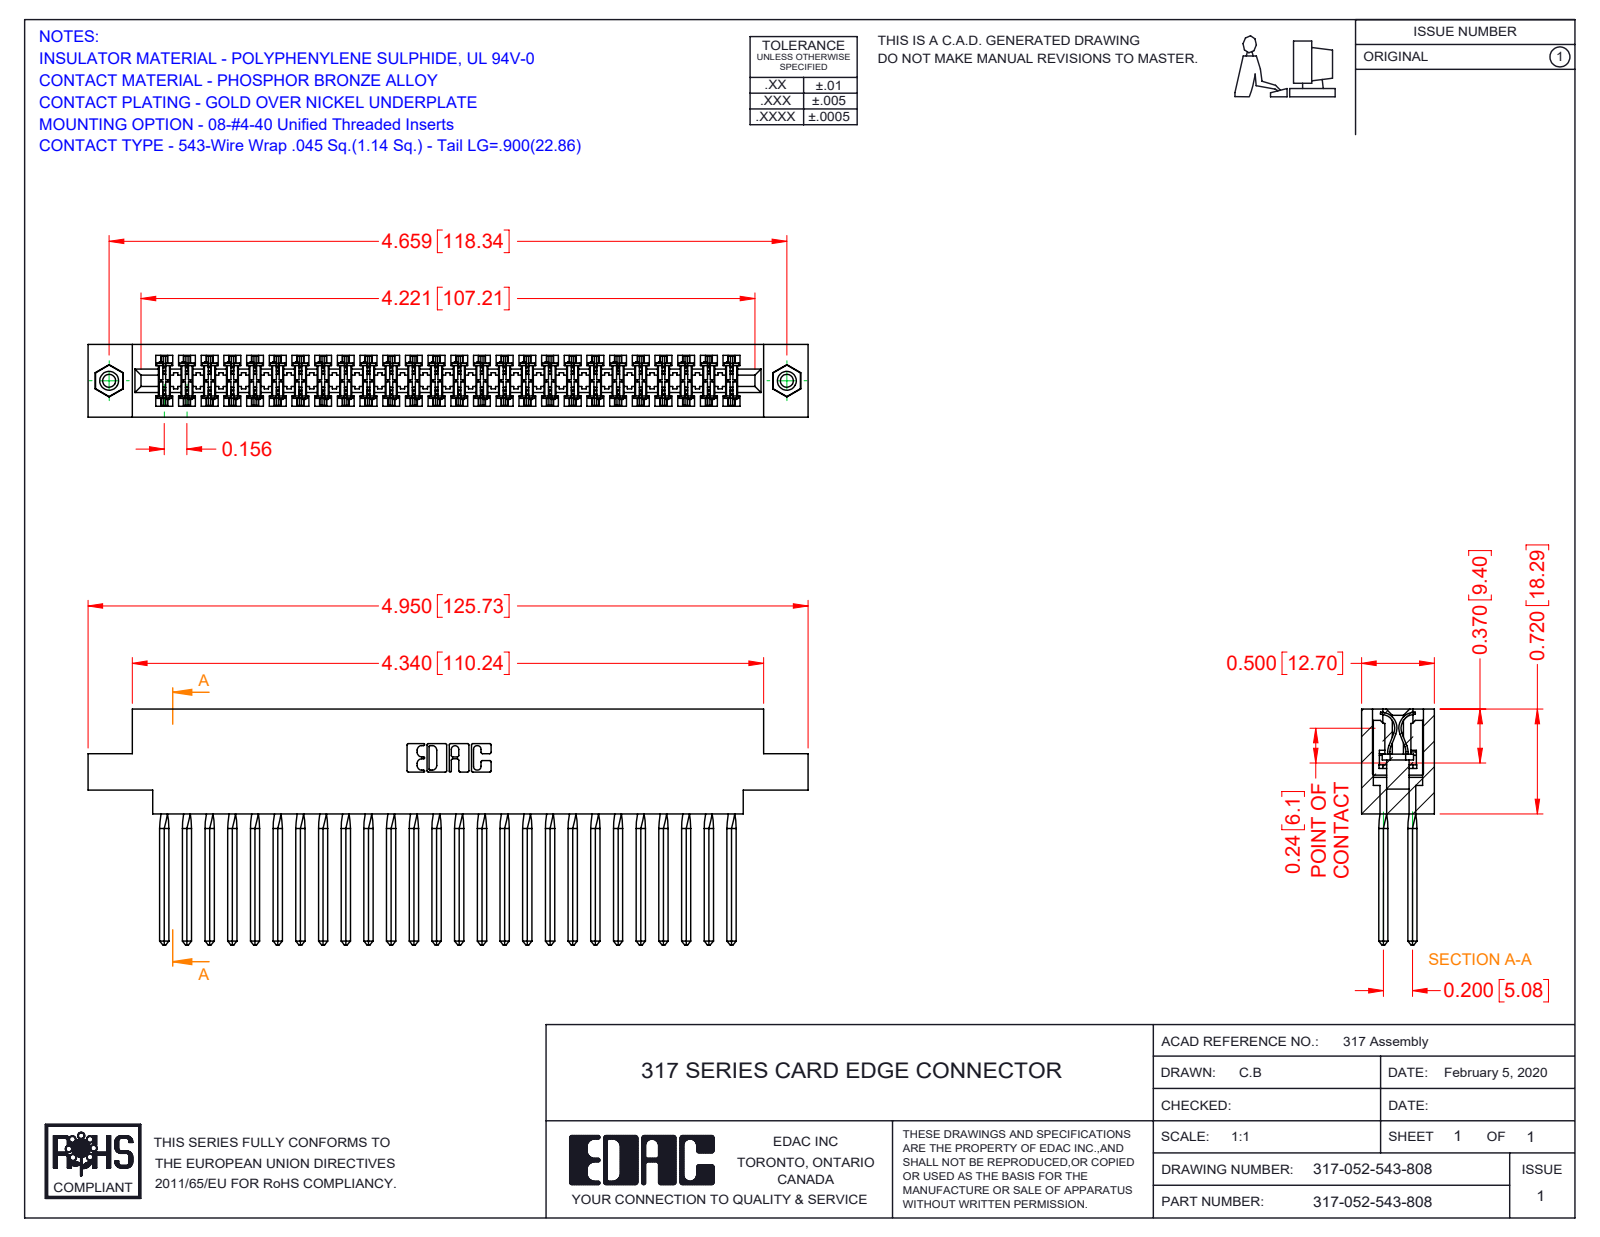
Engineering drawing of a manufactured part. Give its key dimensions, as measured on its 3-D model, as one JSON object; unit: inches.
{"part_name": "317 Part_.156 Dia - TI; 345-250-001_345-250-003-102; 317-290-001_543; 317-052-543-808", "step_written_by": "SolidWorks 2016 (CONFIG_CONTROL_DESIGN)", "units": "inches", "bodies": {"solids": 55, "faces": 4790, "planar": 3886, "cylindrical": 680, "other": 224}, "overall_size": [4.95, 1.62, 0.5], "volume_in3": 1.27, "surface_area_in2": 48, "round_holes": [[0.089, 2], [0.125, 2], [0.156, 2]], "round_bosses_or_shafts": [[0.155, 2]], "partial_cylinders_radius": [[0.015, 104], [0.01, 22], [0.007, 6], [0.031, 6], [0.026, 3], [0.095, 2], [0.1, 2], [0.11, 2]], "face_to_face_distances": [0.5, 0.075, 0.425, 0.11, 0.35, 0.195, 0.094, 0.2, 0.72, 0.115], "hole_center_spacings": [4.659]}
